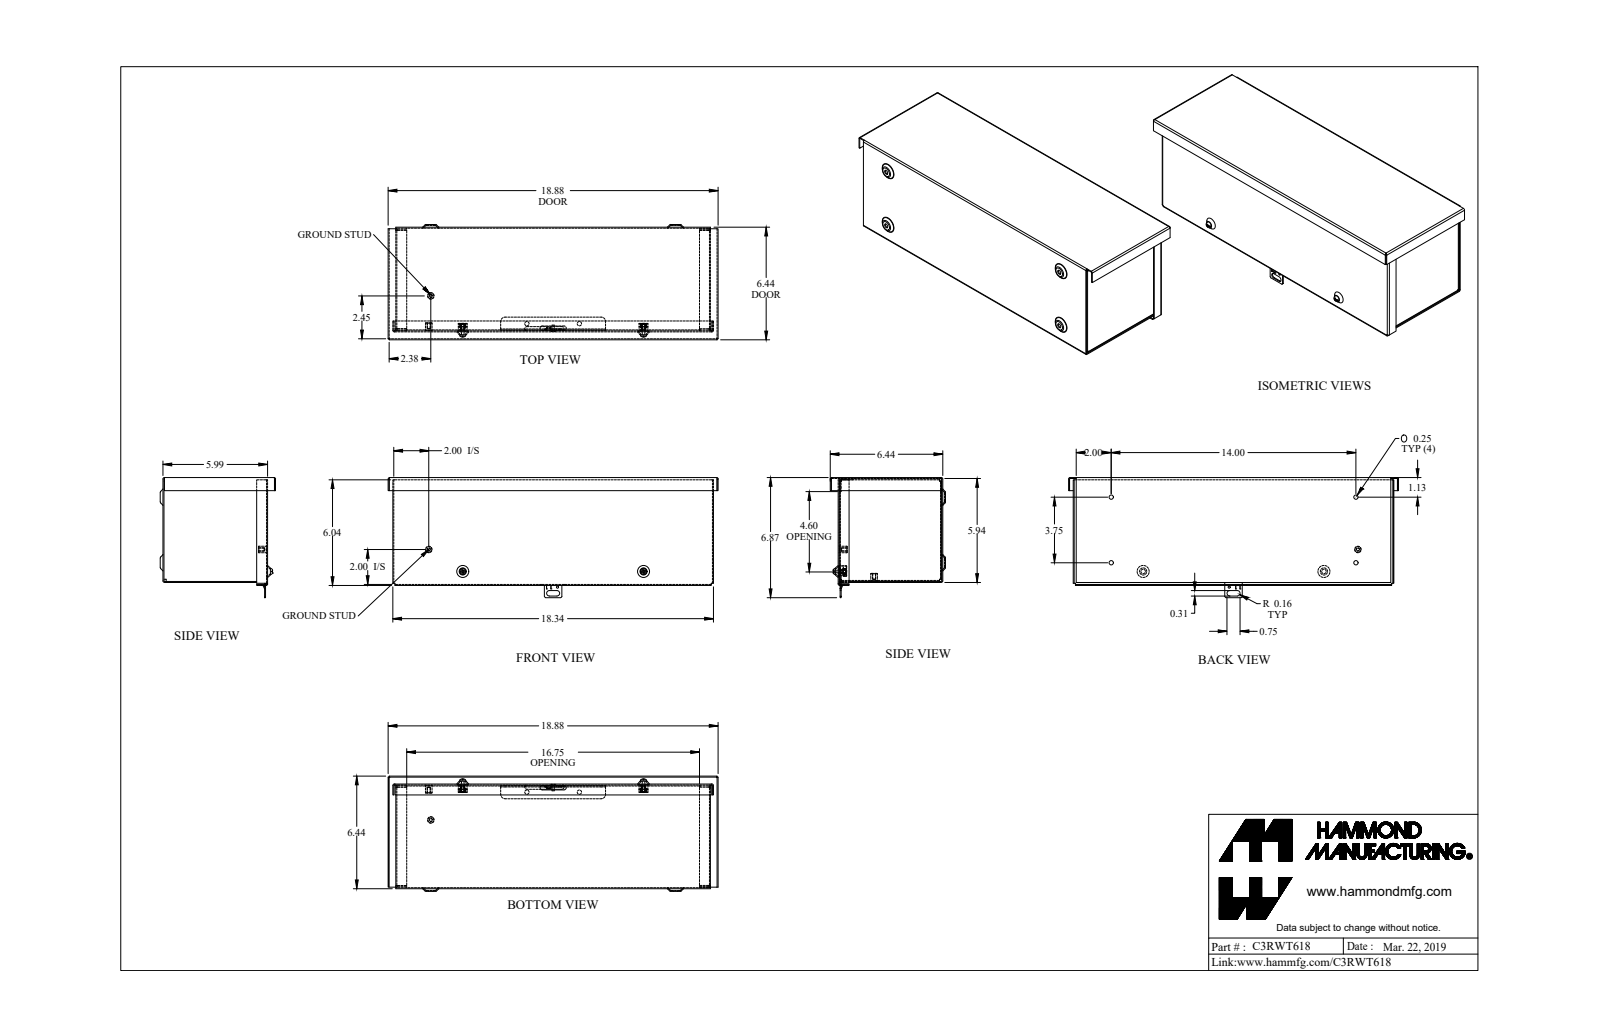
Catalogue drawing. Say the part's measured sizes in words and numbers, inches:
The part is named "C3RWT618_Default". Its 3-D file was written by "SolidWorks 2019 (CONFIG_CONTROL_DESIGN)". It is 19 solids with 645 faces: 344 planar, 201 cylindrical and 100 other. Overall it measures 18.875 by 6.871 by 6.594 inches. Its volume is 34.6 cubic inches and its surface area 1 223 square inches. Round holes: 6 of diameter 0.25, 4 of diameter 0.156, 2 of diameter 0.203, 2 of diameter 0.214, 2 of diameter 0.23, 1 of diameter 0.125, 1 of diameter 0.137, 1 of diameter 0.2, 1 of diameter 0.215. Round bosses or shafts: 3 of diameter 0.19, 2 of diameter 0.375, 2 of diameter 0.148, 1 of diameter 0.5, 1 of diameter 0.367, 1 of diameter 0.21, 1 of diameter 0.152, 1 of diameter 0.125. Partial cylindrical surfaces (rounded edges, fillets, slot ends): 18 of radius 0.029, 18 of radius 0.086, 12 of radius 0.125, 8 of radius 0.08, 8 of radius 0.108, 6 of radius 0.25, 4 of radius 0.016, 4 of radius 0.022. The main face-to-face distances are 0.057, 5.943, 5.928, 5.871, 5.886, 6, 5.985, 17.943, 18, 17.886. The hole center spacings are 1.933, 13.66, 1.895, 2.736, 3.75, 4.626, 5.175, 7.011.
